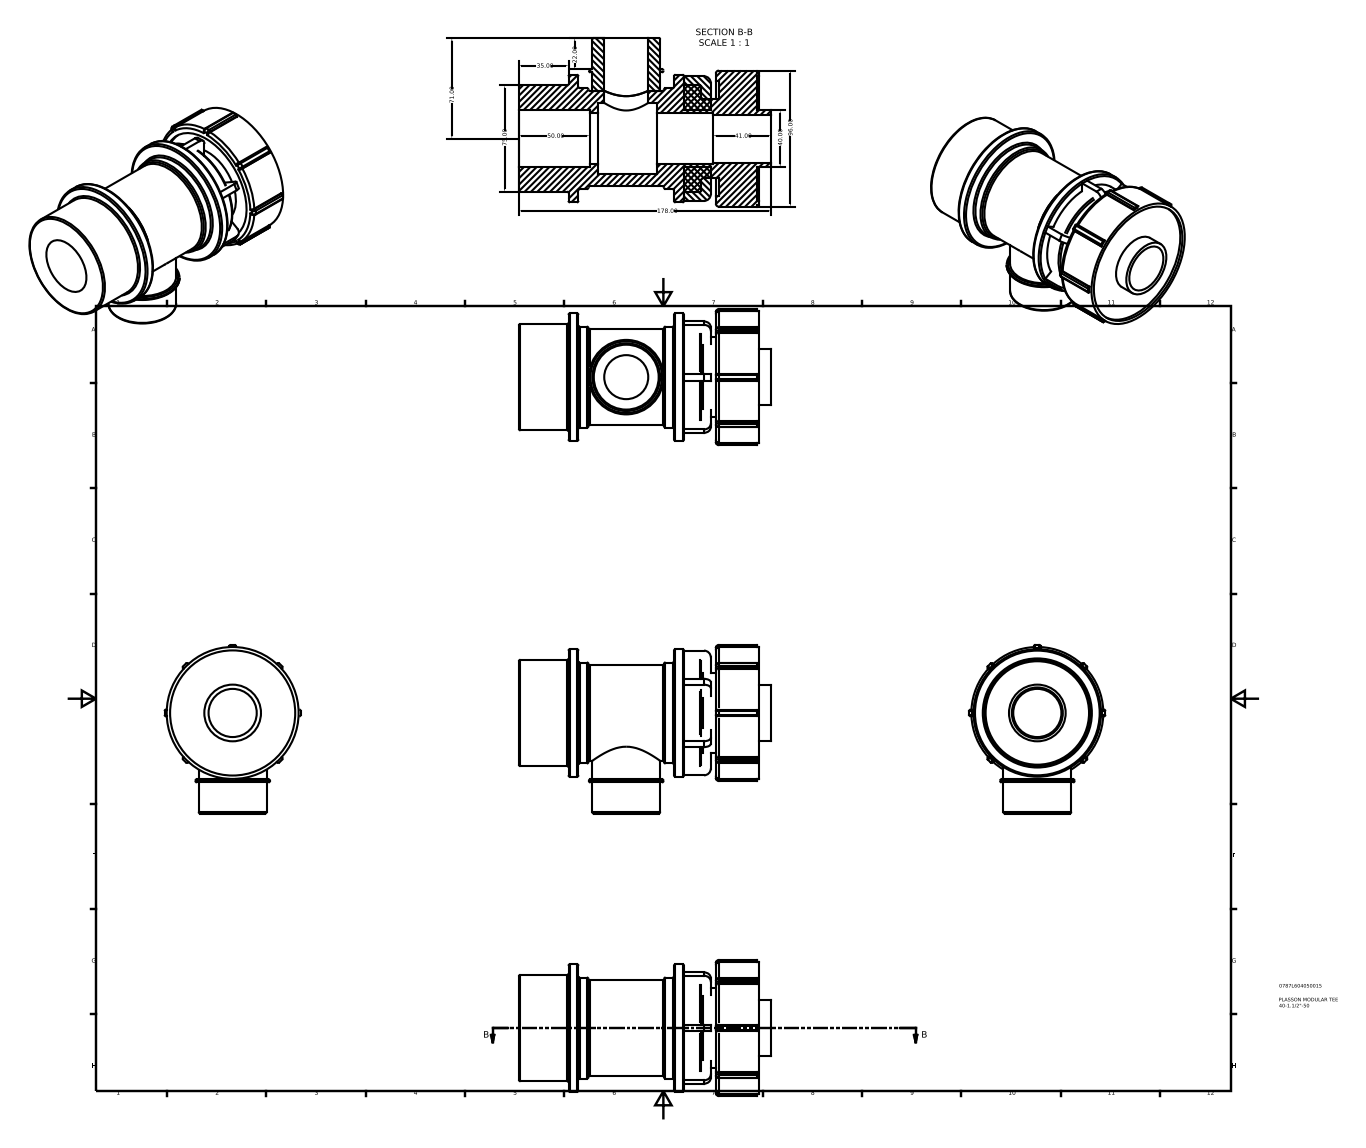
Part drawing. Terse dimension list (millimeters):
name: 0787L604050015
written by: Autodesk Inventor 2015 (AUTOMOTIVE_DESIGN)
unit: mm
bodies: 8 solids, 212 faces (86 planar, 69 cylindrical, 57 other)
size: 178 × 119 × 96
volume: 595 899 mm³; area: 111 527 mm²
holes: 1× ⌀31.07, 1× ⌀34, 1× ⌀36, 1× ⌀40, 1× ⌀50.4, 1× ⌀67.5, 1× ⌀81.6, 1× ⌀88.32
bosses: 1× ⌀93.12, 1× ⌀90, 1× ⌀75, 1× ⌀71.25, 1× ⌀56.25, 1× ⌀52.58, 1× ⌀47.8
rounds: 28× R1, 8× R2, 6× R4.8
face distances: 74.5, 7, 12.3, 167.75, 4.8, 141.1, 26.65, 116.5, 24.6, 51.25
